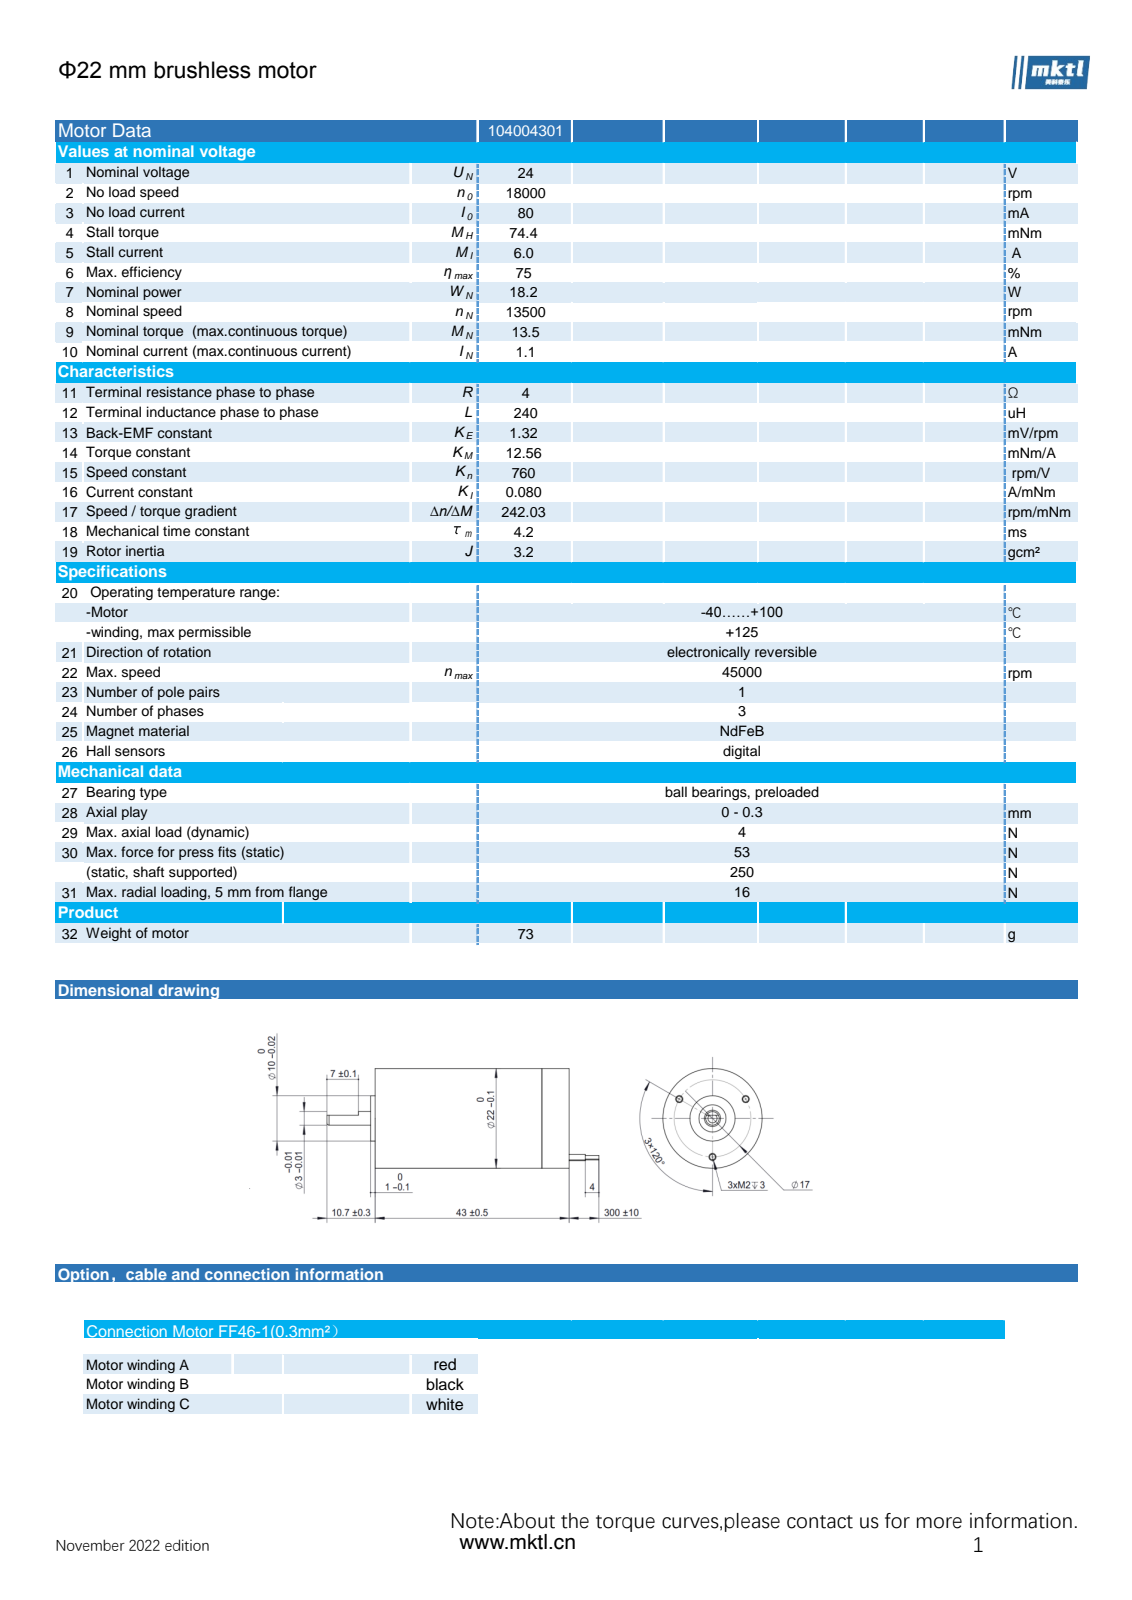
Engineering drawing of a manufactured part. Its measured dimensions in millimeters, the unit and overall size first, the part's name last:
Units: millimetres
Overall size (bounding box): 60.3 × 22 × 22
Round holes (diameter × count): ⌀0.5 ×4, ⌀0.8 ×3, ⌀1.6 ×3, ⌀3 ×1, ⌀3.1 ×1, ⌀6 ×1, ⌀8 ×1, ⌀11.4 ×1, ⌀14.2 ×1, ⌀14.4 ×1, ⌀14.45 ×1, ⌀18.5 ×1
Round bosses / shafts (diameter × count): ⌀1.2 ×3, ⌀0.3 ×3, ⌀22 ×1, ⌀20.9 ×1, ⌀20.8 ×1, ⌀10.4 ×1, ⌀10.3 ×1, ⌀10 ×1
Partial cylindrical surfaces — rounded edges, fillets, slot ends (radius × count): R0.75 ×12, R0.5 ×2, R0.85 ×2, R7.5 ×1, R7.75 ×1, R7.75 ×1, R7.9 ×1, R7.95 ×1
Main face-to-face distances: 0.4, 0.8, 0.6, 1, 1.2, 1.4, 1.6, 1.8, 2.2, 2
Hole centre spacings: 8.25, 8.5, 8.75, 14.72, 1.82, 1.83, 6.38, 10.23
Volume: 14 439 mm³ · Surface area: 56 798 mm²
Bodies: 150 solids, 1116 faces (357 planar, 718 cylindrical, 41 other)
Part name (STEP PRODUCT): 104004301
STEP written by: SolidWorks 2025 (AUTOMOTIVE_DESIGN)
